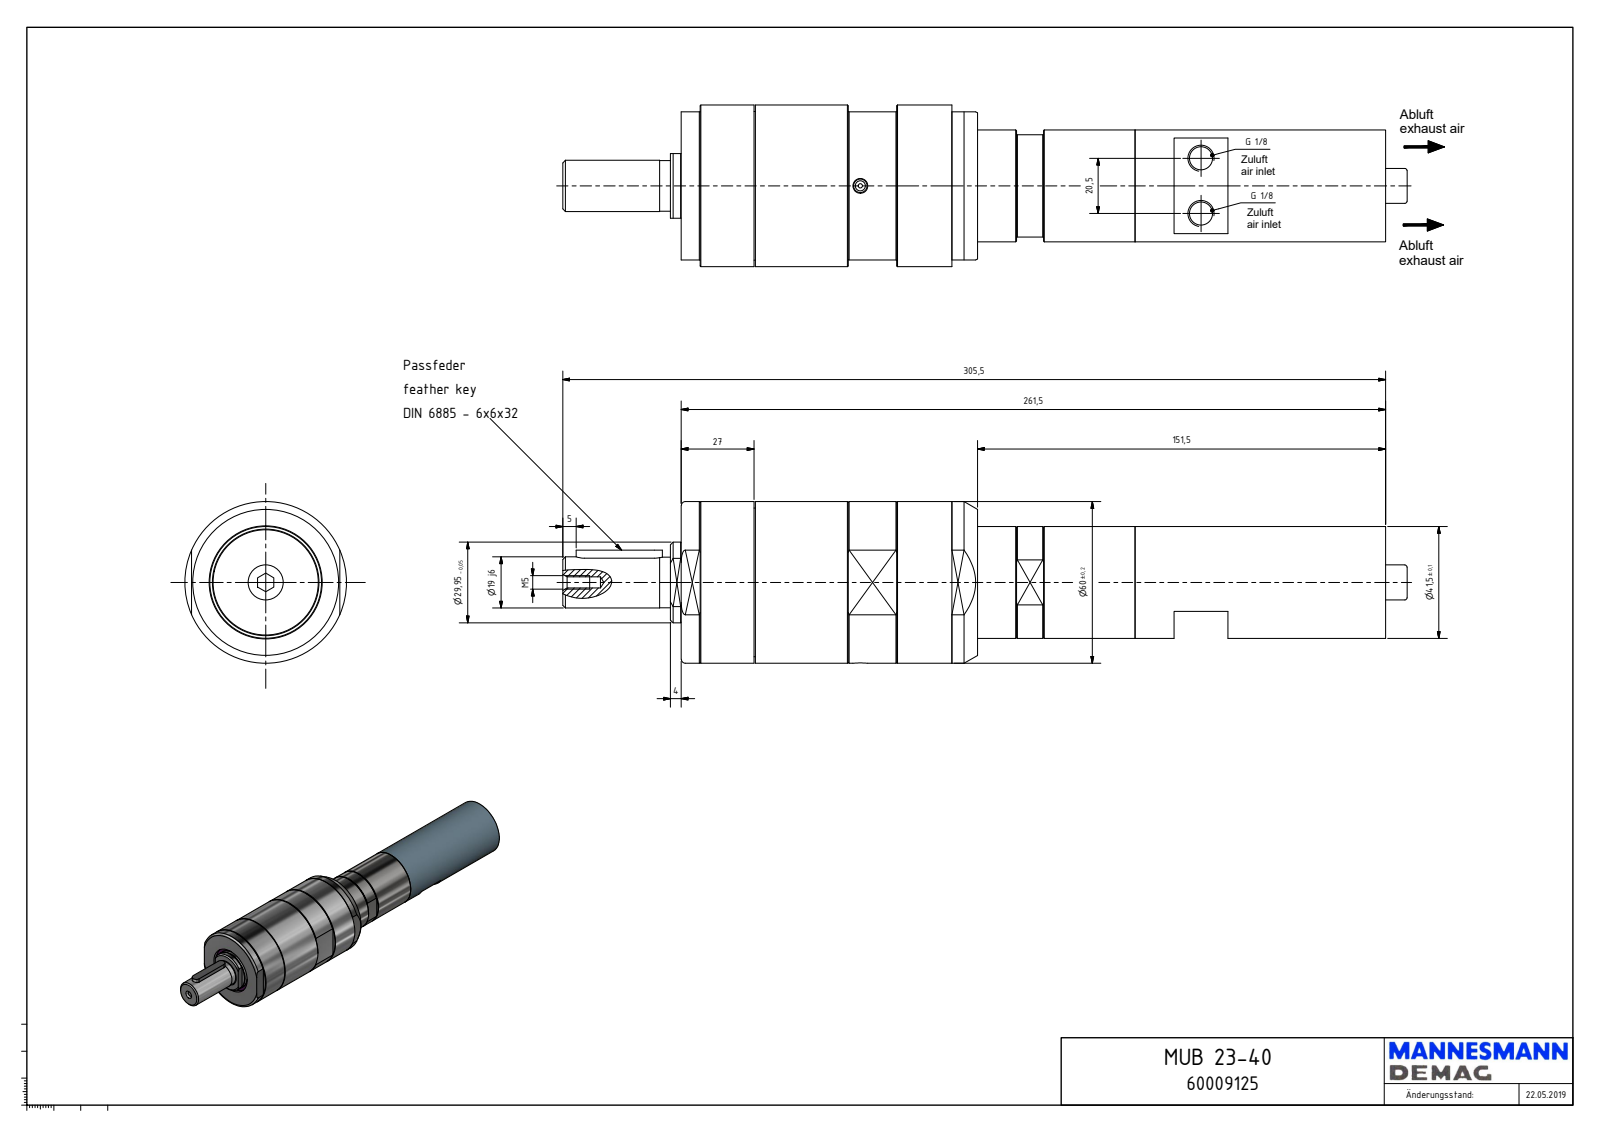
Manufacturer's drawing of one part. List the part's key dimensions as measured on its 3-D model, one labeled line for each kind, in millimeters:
Part name (STEP PRODUCT): MUB 23-40_60009125
STEP written by: Autodesk Inventor 2018 (AUTOMOTIVE_DESIGN)
Units: millimetres
Bodies: 1 solid, 171 faces (75 planar, 58 cylindrical, 38 other)
Overall size (bounding box): 313.5 × 60 × 60
Volume: 518 518 mm³ · Surface area: 56 819 mm²
Round holes (diameter × count): ⌀8.57 ×2, ⌀1.55 ×1, ⌀4 ×1, ⌀4.13 ×1, ⌀5.5 ×1, ⌀8.5 ×1, ⌀35 ×1, ⌀39.5 ×1, ⌀42 ×1, ⌀55.38 ×1
Round bosses / shafts (diameter × count): ⌀60 ×1, ⌀55.18 ×1, ⌀41.5 ×1, ⌀39 ×1, ⌀36.16 ×1, ⌀29.95 ×1, ⌀19 ×1, ⌀18.8 ×1
Partial cylindrical surfaces — rounded edges, fillets, slot ends (radius × count): R1 ×2, R1.6 ×2, R2 ×2, R2.5 ×2, R3 ×2, R8 ×1, R8.1 ×1, R12.91 ×1
Main face-to-face distances: 261.5, 110, 151.5, 55, 78.5, 82.5, 27.5, 234, 104.5, 31
Hole centre spacings: 126.91, 20.5
